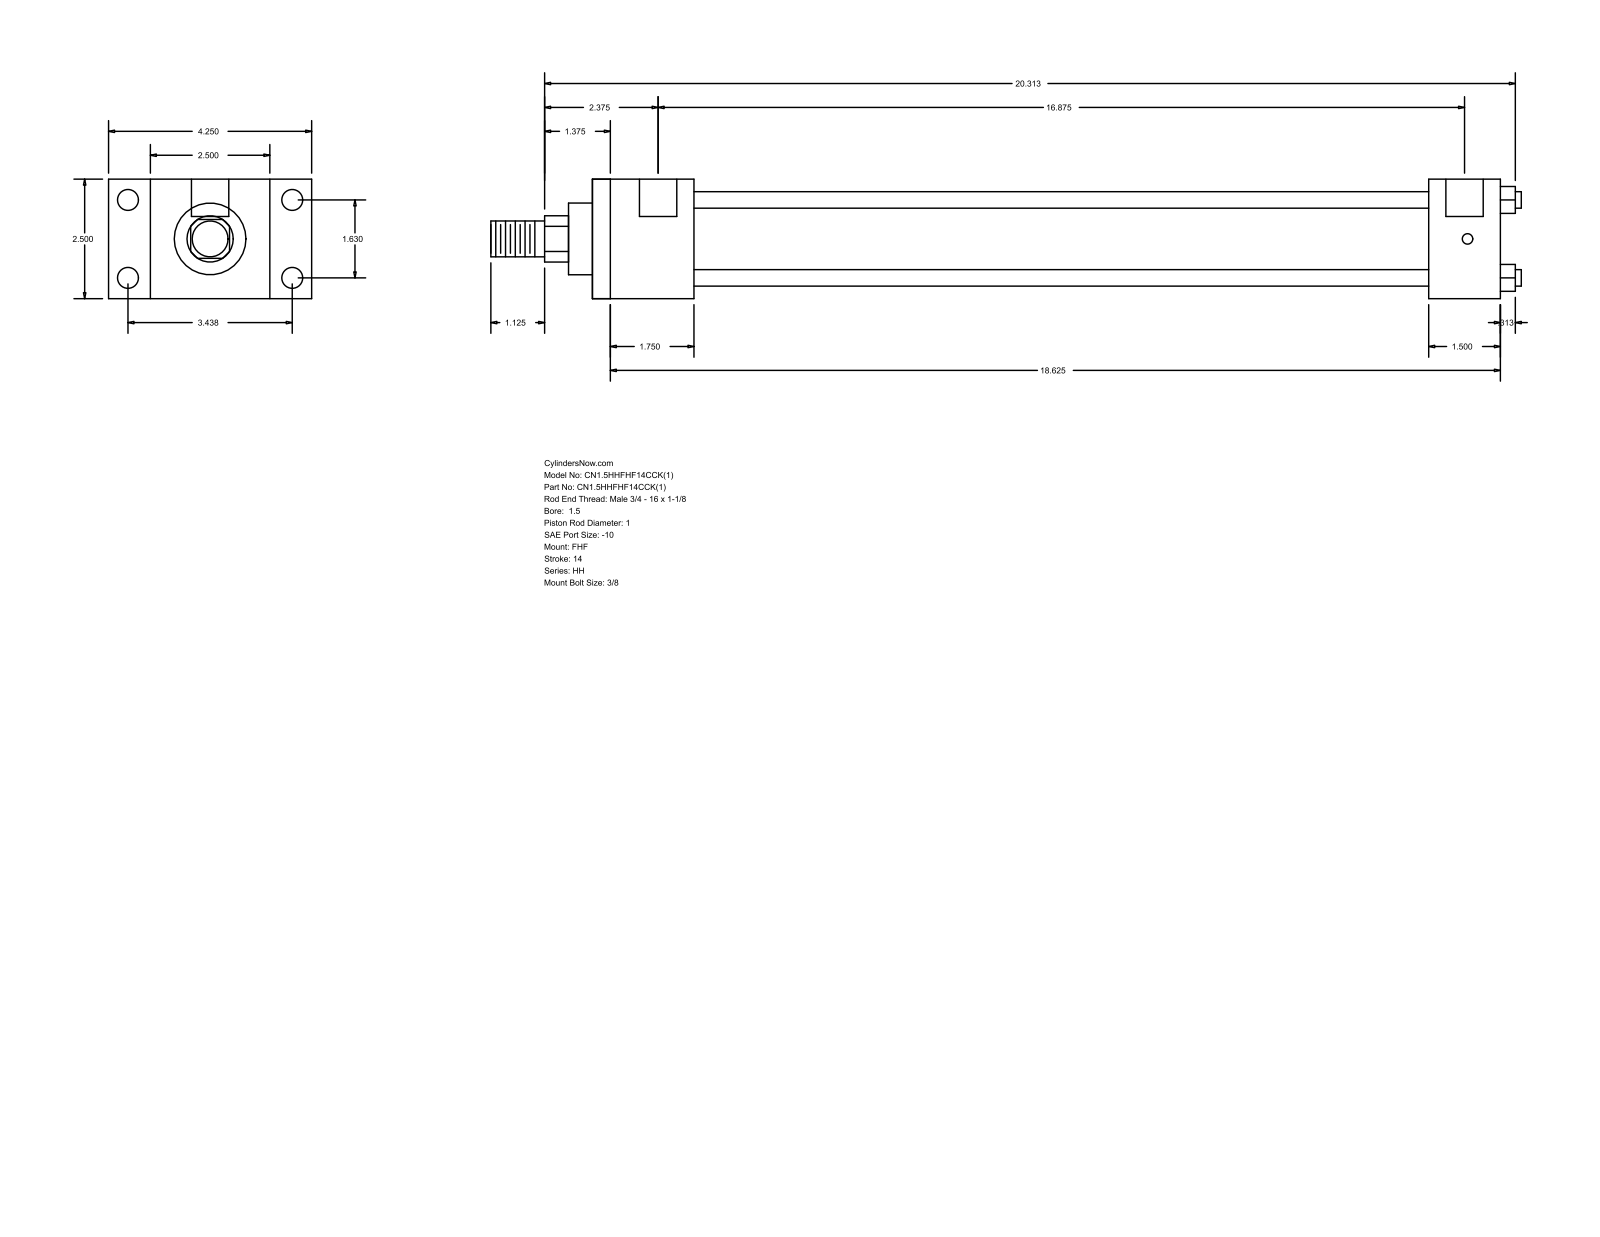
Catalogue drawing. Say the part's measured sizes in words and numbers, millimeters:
The part is named "HH_FHF__0150_1". Its 3-D file was written by "GSSL Pune (CONFIG_CONTROL_DESIGN)". It is 0 solids with 88 faces: 60 planar, 28 cylindrical and 0 other. Overall it measures 547.69 by 107.95 by 63.5 millimeters. Round holes: 4 of diameter 5.56, 4 of diameter 11.13, 2 of diameter 19.84. Round bosses or shafts: 4 of diameter 8.76, 1 of diameter 44.45, 1 of diameter 38.1, 1 of diameter 25.4, 1 of diameter 19.05. Partial cylindrical surfaces (rounded edges, fillets, slot ends): 1 of radius 12.29. The main face-to-face distances are 63.5, 22.23, 85.73, 53.98, 107.96, 482.6, 428.62, 38.1, 444.5, 390.52. The hole center spacings are 1.59, 41.4, 87.32, 96.64, 430.21, 431.8, 428.62.
